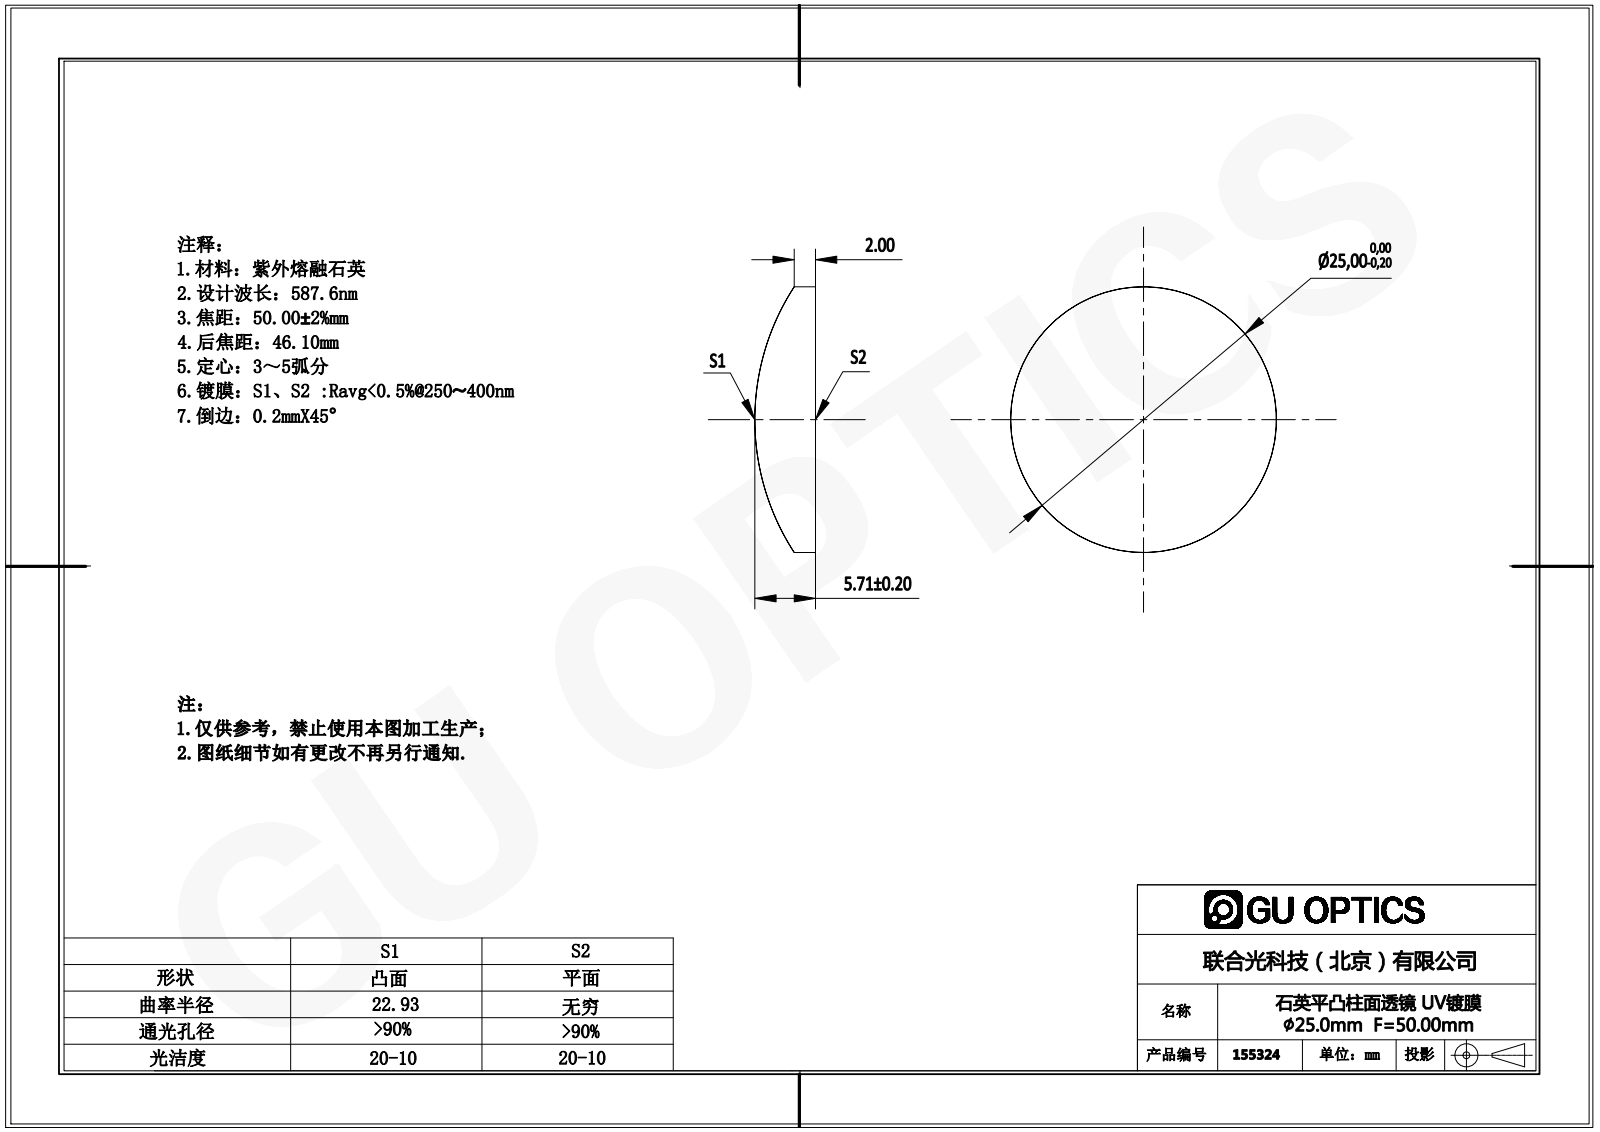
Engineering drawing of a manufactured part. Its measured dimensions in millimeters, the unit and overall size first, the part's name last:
Units: millimetres
Overall size (bounding box): 25 × 25 × 5.71
Round bosses / shafts (diameter × count): ⌀25 ×1
Partial cylindrical surfaces — rounded edges, fillets, slot ends (radius × count): R22.93 ×1
Volume: 2 368 mm³ · Surface area: 1 308 mm²
Bodies: 1 solid, 4 faces (1 planar, 3 cylindrical, 0 other)
Part name (STEP PRODUCT): 155290
STEP written by: SolidWorks 2016 (AUTOMOTIVE_DESIGN)
